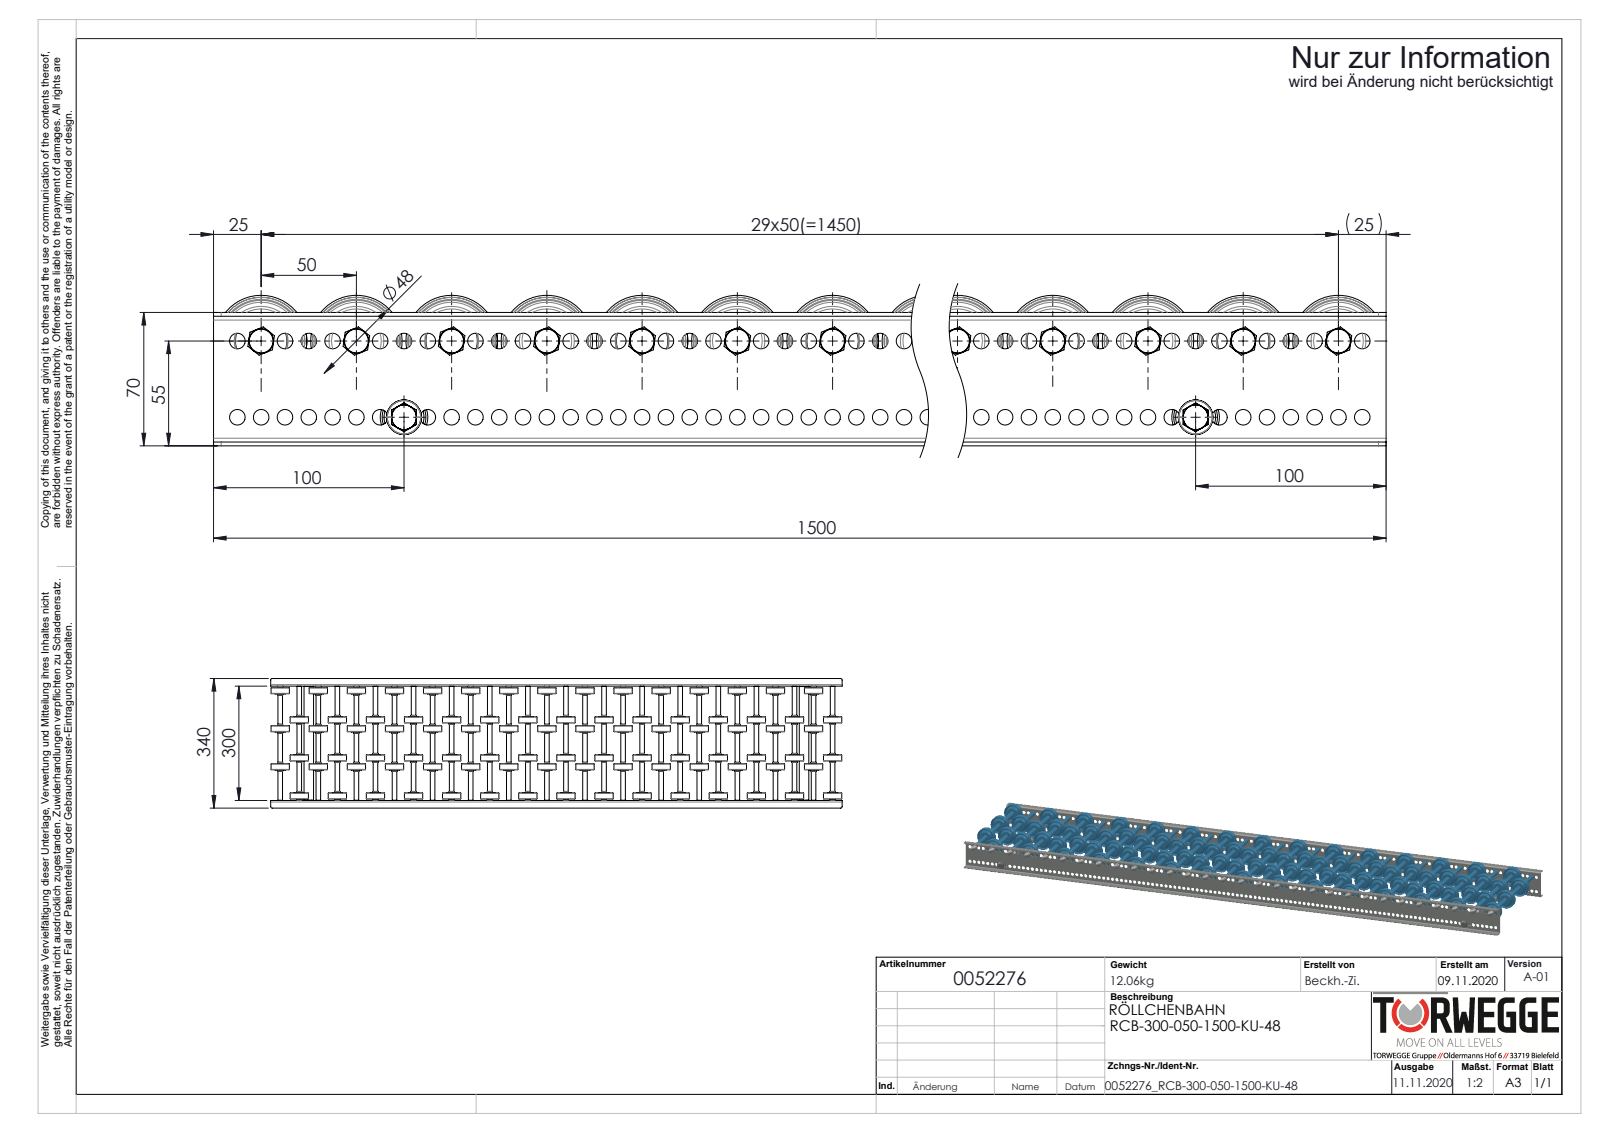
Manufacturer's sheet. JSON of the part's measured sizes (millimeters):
{"part_name": "Profil_LRB-20x70x20x2_KFG_S100201_U-PROFIL-20-70-20-2-LRB-L=1500; 0052276; S106837_Gewindestange-M8-KFG_L320; S100994_Sperrzahnschraube_M08x16-8.8-A2K (+5 more)", "step_written_by": "SolidWorks 2020 (AUTOMOTIVE_DESIGN)", "units": "millimeters", "bodies": {"solids": 282, "faces": 9902, "planar": 1830, "cylindrical": 3288, "other": 4784}, "overall_size": [1500, 340, 79], "volume_mm3": 3221000, "surface_area_mm2": 2343000, "round_holes": [[8.2, 238], [6.65, 30], [9.65, 30], [13.7, 30], [6.8, 2], [21, 2]], "round_bosses_or_shafts": [[8, 32], [48, 30], [27, 30], [12.7, 30], [12.5, 30], [12, 30], [25, 2]], "partial_cylinders_radius": [[4, 8], [2, 4]], "face_to_face_distances": [2, 302, 68, 304, 300, 99.8, 70, 66, 16.3, 76.1], "hole_center_spacings": [12.5, 25, 37.5, 50, 62.5, 75, 87.5, 100]}
